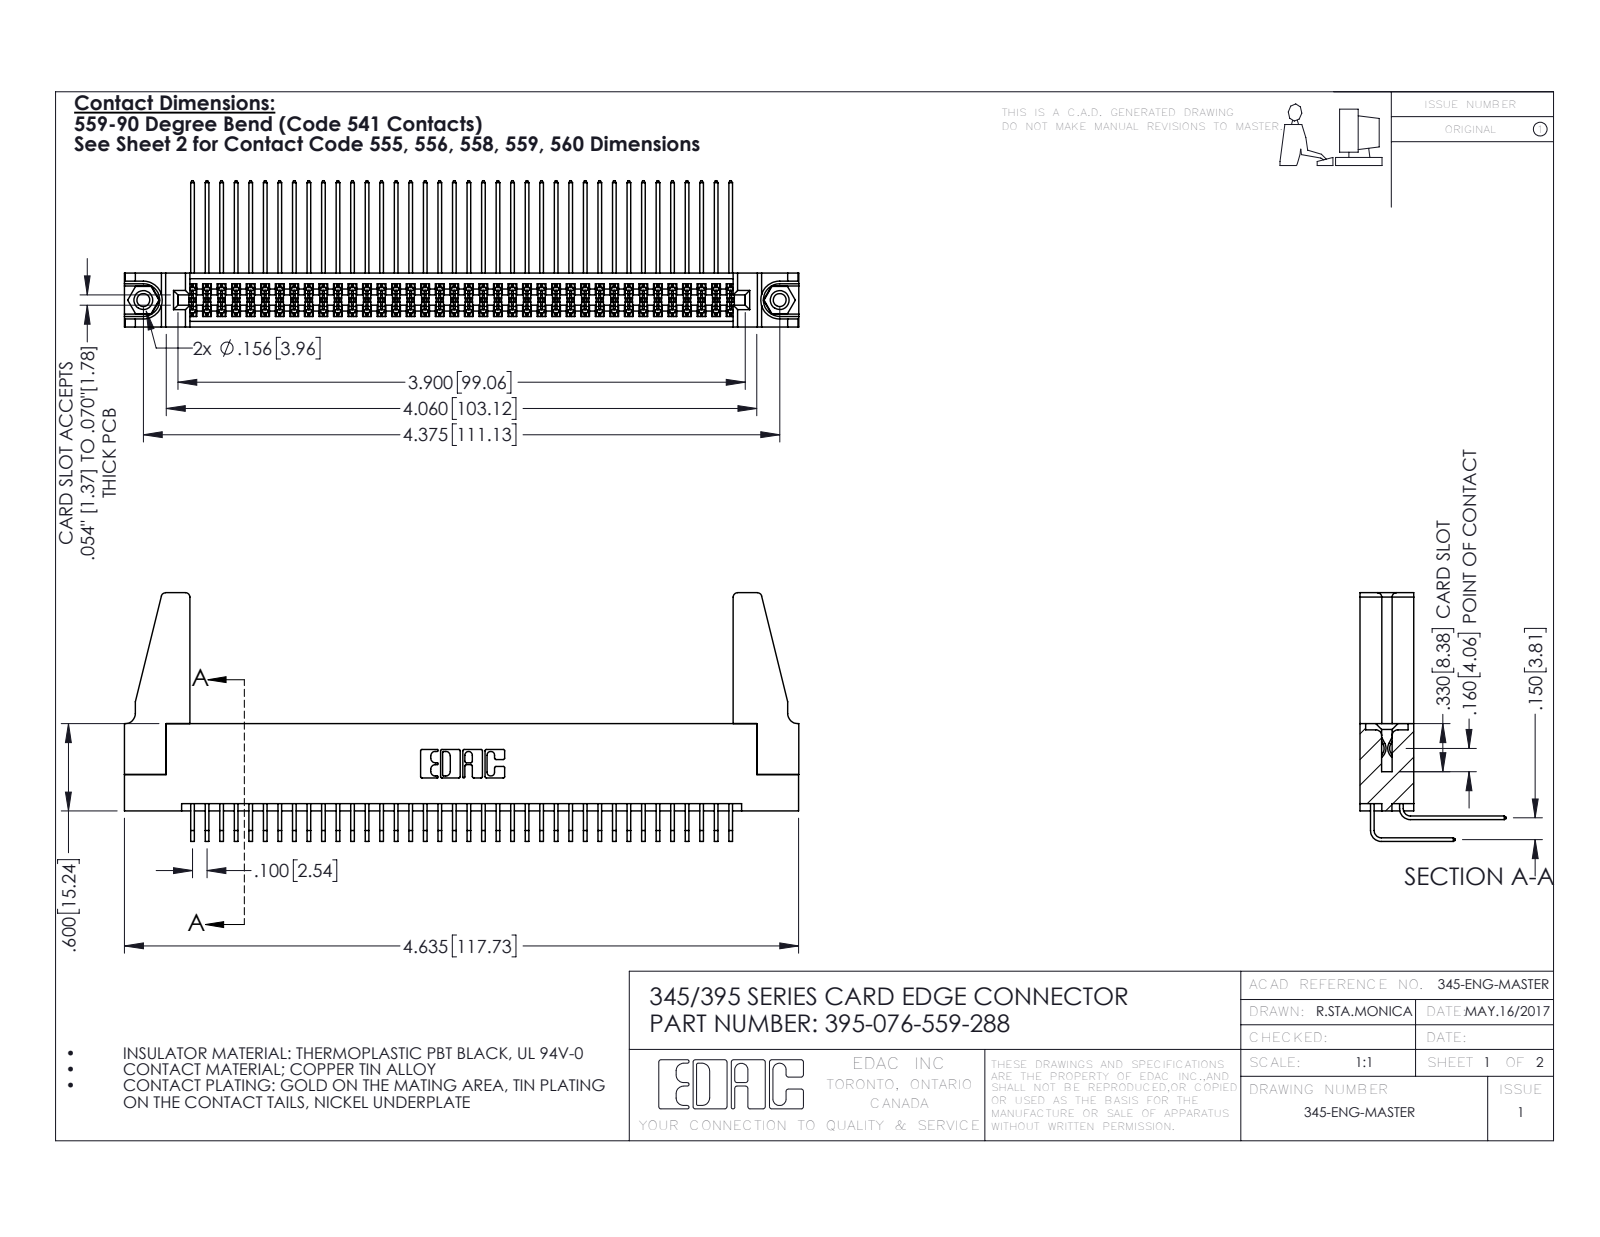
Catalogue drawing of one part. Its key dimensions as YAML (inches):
part_name: "345 Part_Flush Mounting Lugs - 0.156 Dia-TH; 395-076-559-288; 345-292-001_558 559 Tail - 1; 345-220-078_345-220-088 (+2 more)"
step_written_by: "SolidWorks 2016 (CONFIG_CONTROL_DESIGN)"
units: inches
bodies: {solids: 81, faces: 4202, planar: 2812, cylindrical: 1374, other: 16}
overall_size: [4.636, 1.709, 1.005]
volume: 0.921
surface_area: 35.04
round_holes:
  - {diameter: 0.089, count: 2}
  - {diameter: 0.125, count: 2}
  - {diameter: 0.156, count: 2}
  - {diameter: 0.064, count: 1}
round_bosses_or_shafts:
  - {diameter: 0.155, count: 2}
partial_cylinders:
  - {radius: 0.006, count: 114}
  - {radius: 0.01, count: 22}
  - {radius: 0.03, count: 8}
  - {radius: 0.007, count: 6}
  - {radius: 0.031, count: 6}
  - {radius: 0.026, count: 3}
  - {radius: 0.014, count: 2}
  - {radius: 0.019, count: 2}
face_to_face_distances: [0.072, 0.298, 0.37, 0.2, 0.098, 0.272, 0.025, 0.225, 0.175, 0.15]
hole_center_spacings: [0.27, 4.139, 4.375]
